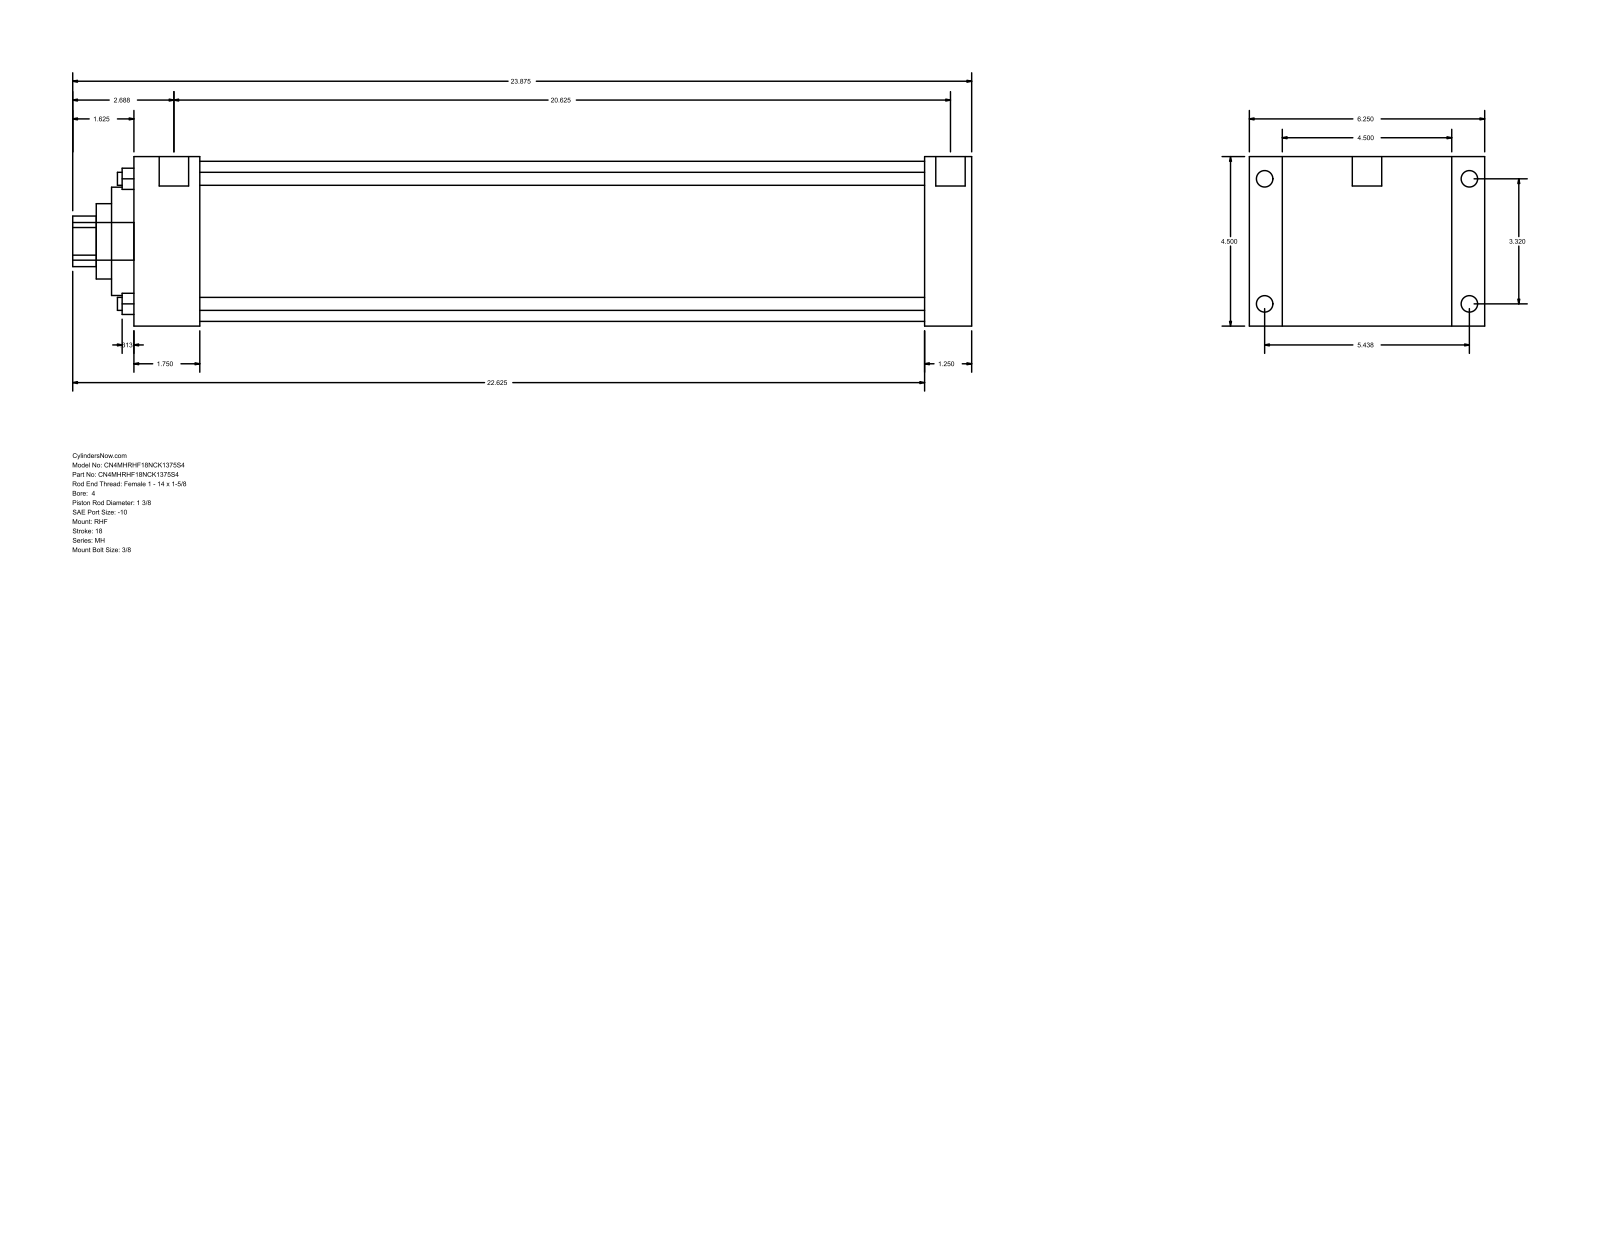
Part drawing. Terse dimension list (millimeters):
name: MH_RHF__0400_1.375
written by: GSSL Pune (CONFIG_CONTROL_DESIGN)
unit: mm
bodies: 0 solids, 90 faces (61 planar, 29 cylindrical, 0 other)
size: 606.42 × 158.75 × 114.3
holes: 4× ⌀8.76, 1× ⌀34.92, 1× ⌀50.8, 1× ⌀73.03, 1× ⌀107.95
bosses: 4× ⌀11.13, 4× ⌀8.73, 2× ⌀19.84, 1× ⌀25.4
rounds: 1× R17.06
face distances: 114.3, 565.15, 533.4, 31.75, 22.23, 136.53, 44.45, 488.95, 520.7, 158.76
hole spacings: 59.62, 84.32, 119.25
